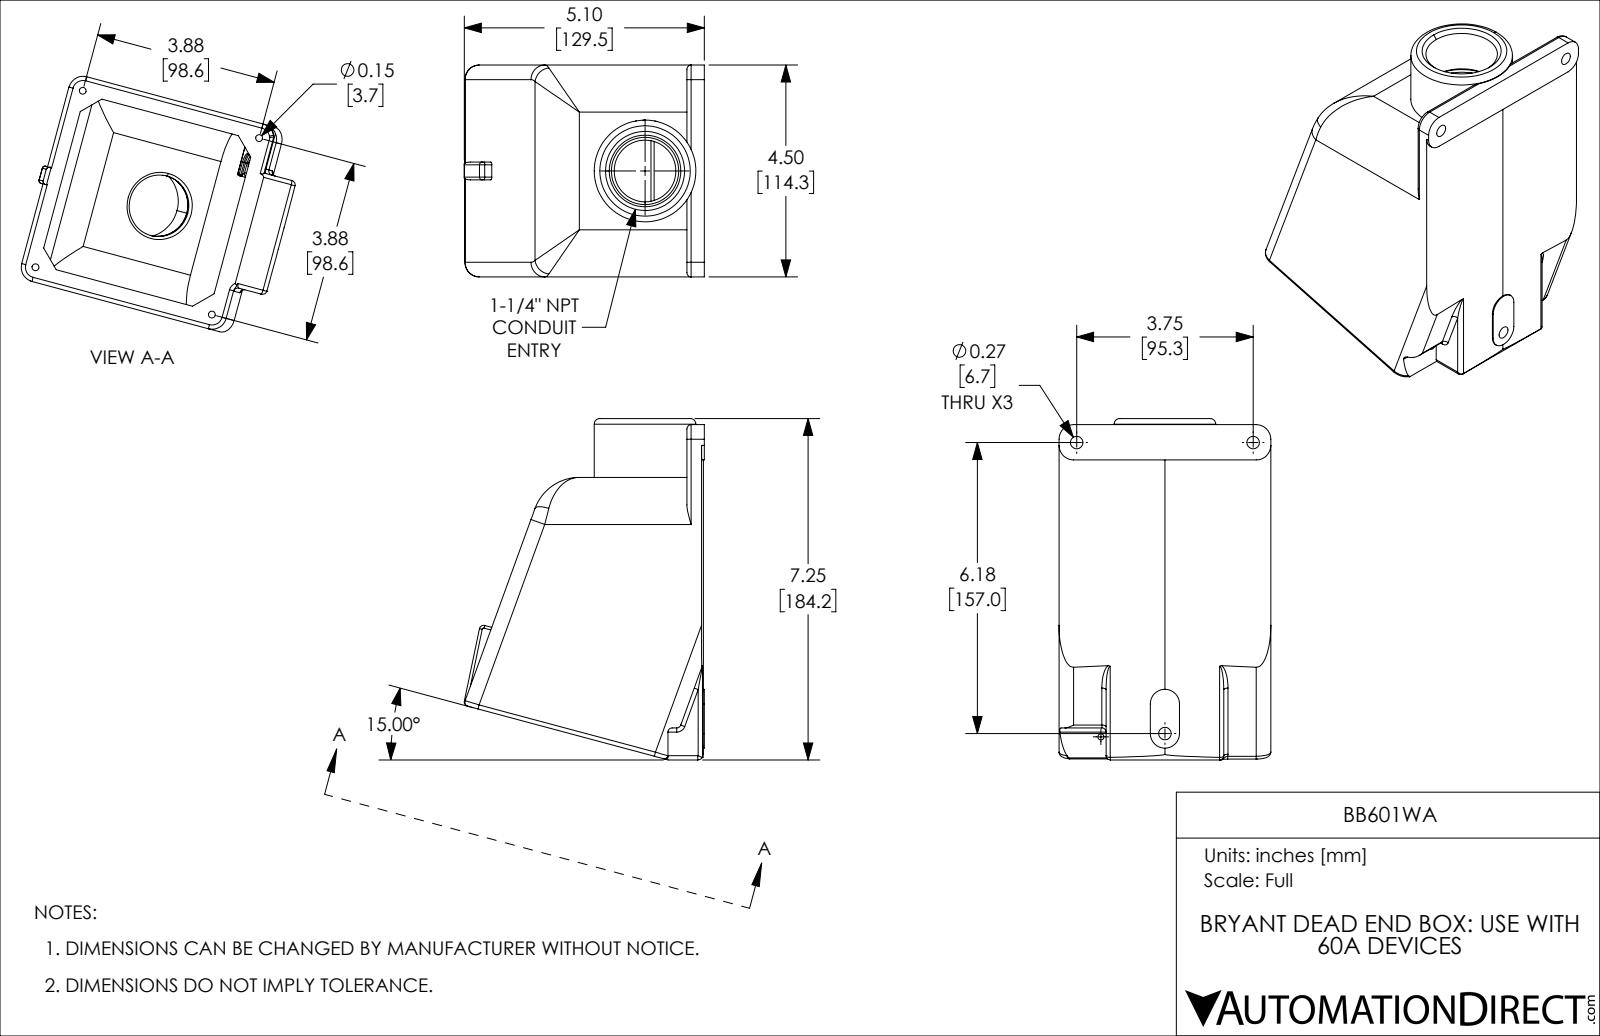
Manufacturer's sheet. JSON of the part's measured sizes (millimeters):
{"part_name": "BB601WA", "step_written_by": "SolidWorks 2021 (CONFIG_CONTROL_DESIGN)", "units": "millimeters", "bodies": {"solids": 1, "faces": 356, "planar": 115, "cylindrical": 179, "other": 62}, "overall_size": [184.2, 129.6, 114.3], "volume_mm3": 386100, "surface_area_mm2": 153500, "round_holes": [[3.7, 4], [6.7, 2], [14.2, 2], [3.3, 1], [6.7, 1], [33.3, 1], [38.6, 1], [43.7, 1]], "round_bosses_or_shafts": [[54.9, 1]], "partial_cylinders_radius": [[2.3, 40], [7.9, 10], [0.8, 6], [1.5, 4], [6.4, 4], [20.6, 3], [25.4, 3], [2.9, 1]], "face_to_face_distances": [4.8, 109.5, 104.6, 114.3, 109.1, 5.3, 113.5, 108.7, 4.1, 0.8], "hole_center_spacings": [98.6, 98.6, 139.4, 164, 25.4, 34.6, 95.3, 159.3]}
